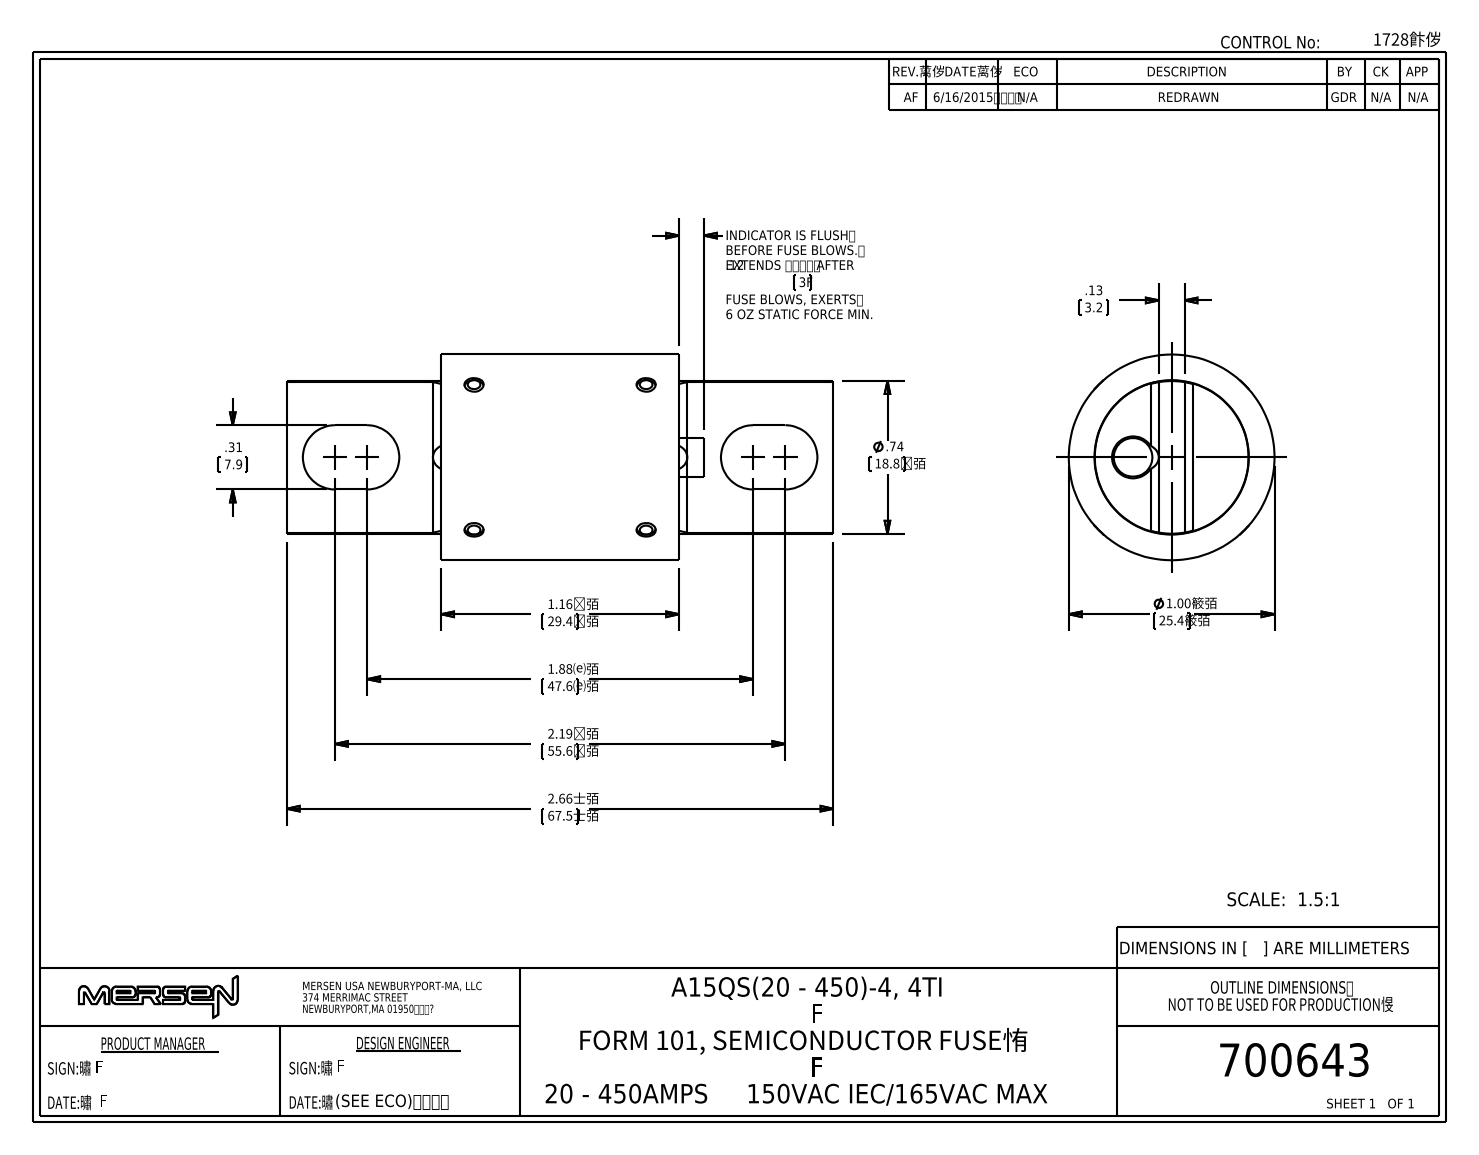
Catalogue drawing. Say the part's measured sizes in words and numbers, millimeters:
The part is named "700643revA". Its 3-D file was written by "SolidWorks 2014 (AUTOMOTIVE_DESIGN)". It is 0 solids with 92 faces: 28 planar, 40 cylindrical and 24 other. Overall it measures 67.5 by 25.4 by 25.4 millimeters. Round holes: 4 of diameter 2.4, 1 of diameter 4.7, 1 of diameter 19.1. Round bosses or shafts: 1 of diameter 25.4, 1 of diameter 19. Partial cylindrical surfaces (rounded edges, fillets, slot ends): 4 of radius 4, 1 of radius 9.4. The main face-to-face distances are 3.2, 29.4, 19.1, 48.4, 67.5, 24.4, 7.9, 25.4. The hole center spacings are 21.2, 4.7.
